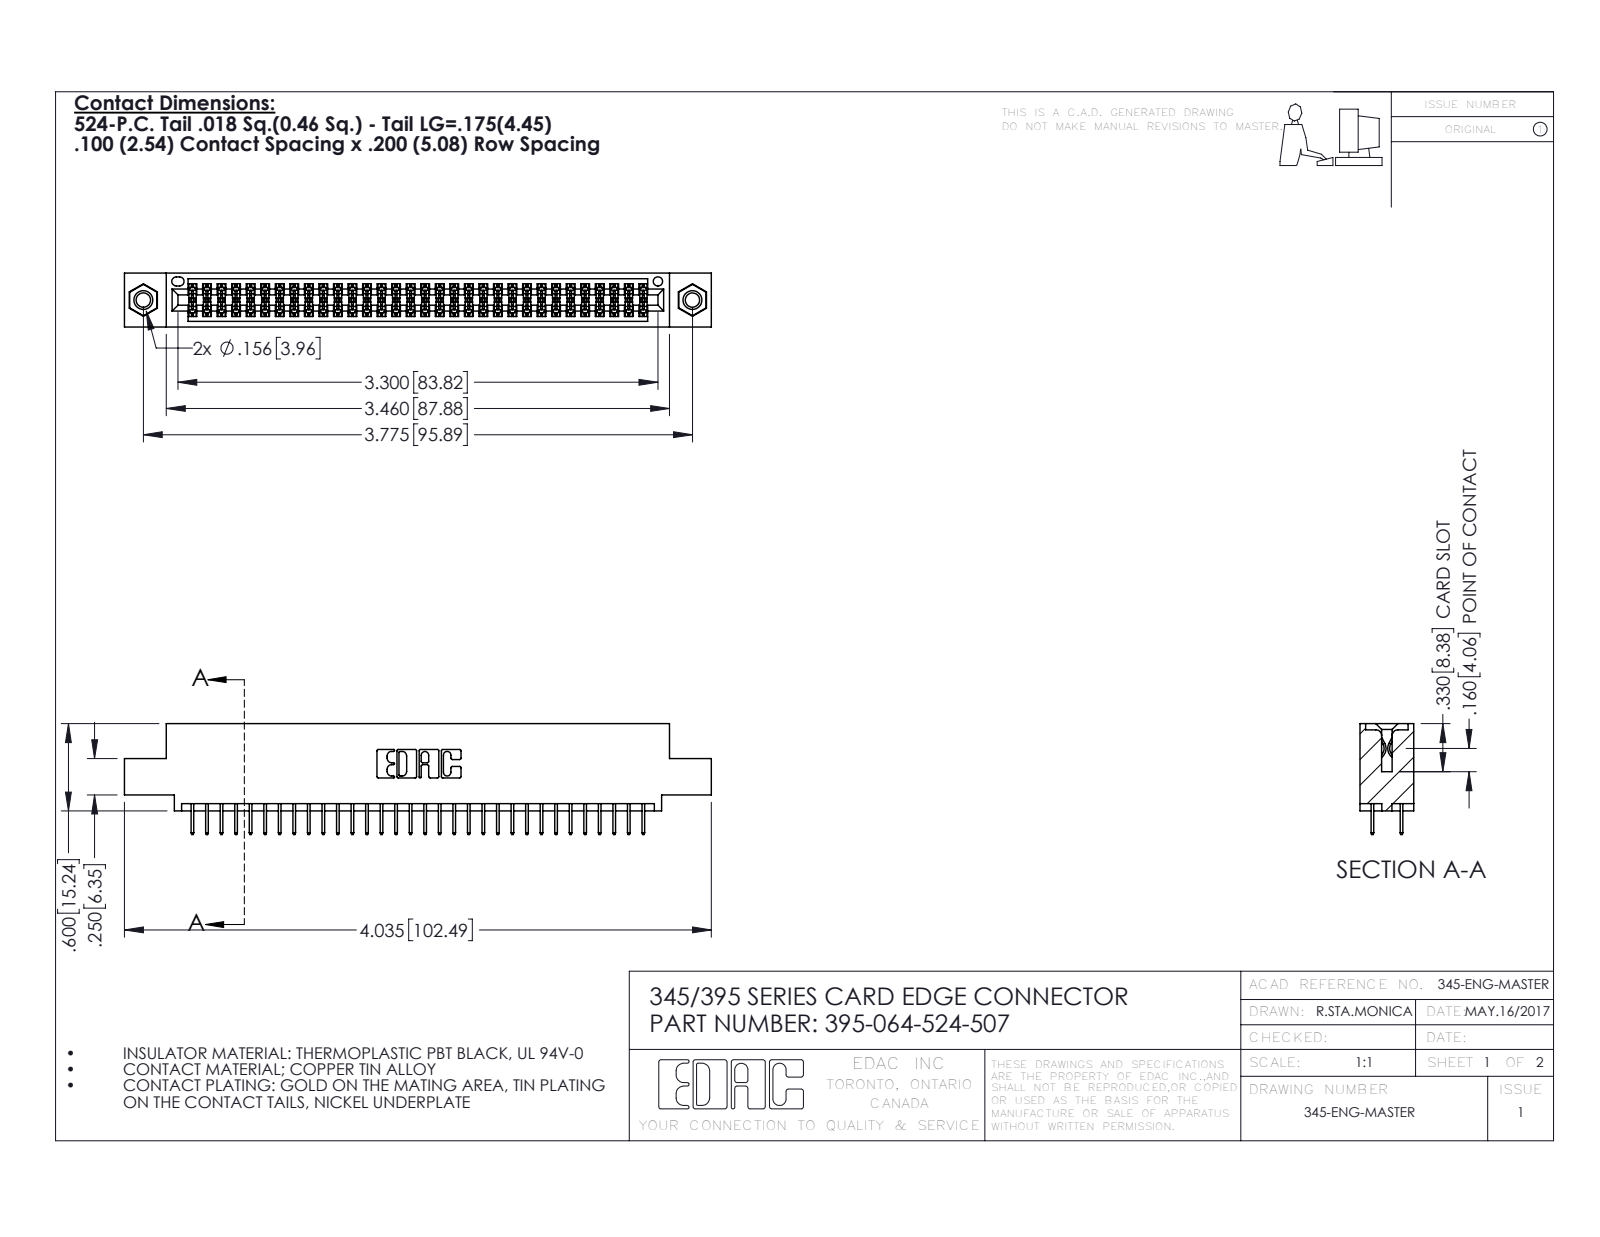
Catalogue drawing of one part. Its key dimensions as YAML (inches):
part_name: "345-250-001_345-250-005-103; 345 Part_0.110 Offset - 0.156 Dia-TI; 395-064-524-507; 345-292-001_345-293-124"
step_written_by: "SolidWorks 2016 (CONFIG_CONTROL_DESIGN)"
units: inches
bodies: {solids: 67, faces: 3646, planar: 2612, cylindrical: 1018, other: 16}
overall_size: [4.035, 0.762, 0.37]
volume: 0.591
surface_area: 21.67
round_holes:
  - {diameter: 0.098, count: 2}
  - {diameter: 0.125, count: 2}
  - {diameter: 0.156, count: 2}
  - {diameter: 0.064, count: 1}
round_bosses_or_shafts:
  - {diameter: 0.155, count: 2}
partial_cylinders:
  - {radius: 0.006, count: 96}
  - {radius: 0.01, count: 22}
  - {radius: 0.007, count: 6}
  - {radius: 0.031, count: 6}
  - {radius: 0.026, count: 3}
  - {radius: 0.014, count: 2}
  - {radius: 0.019, count: 2}
  - {radius: 0.022, count: 2}
face_to_face_distances: [0.072, 0.298, 0.2, 0.37, 0.098, 0.272, 0.025, 0.225, 0.072, 0.175]
hole_center_spacings: [0.27, 3.54, 3.775]
